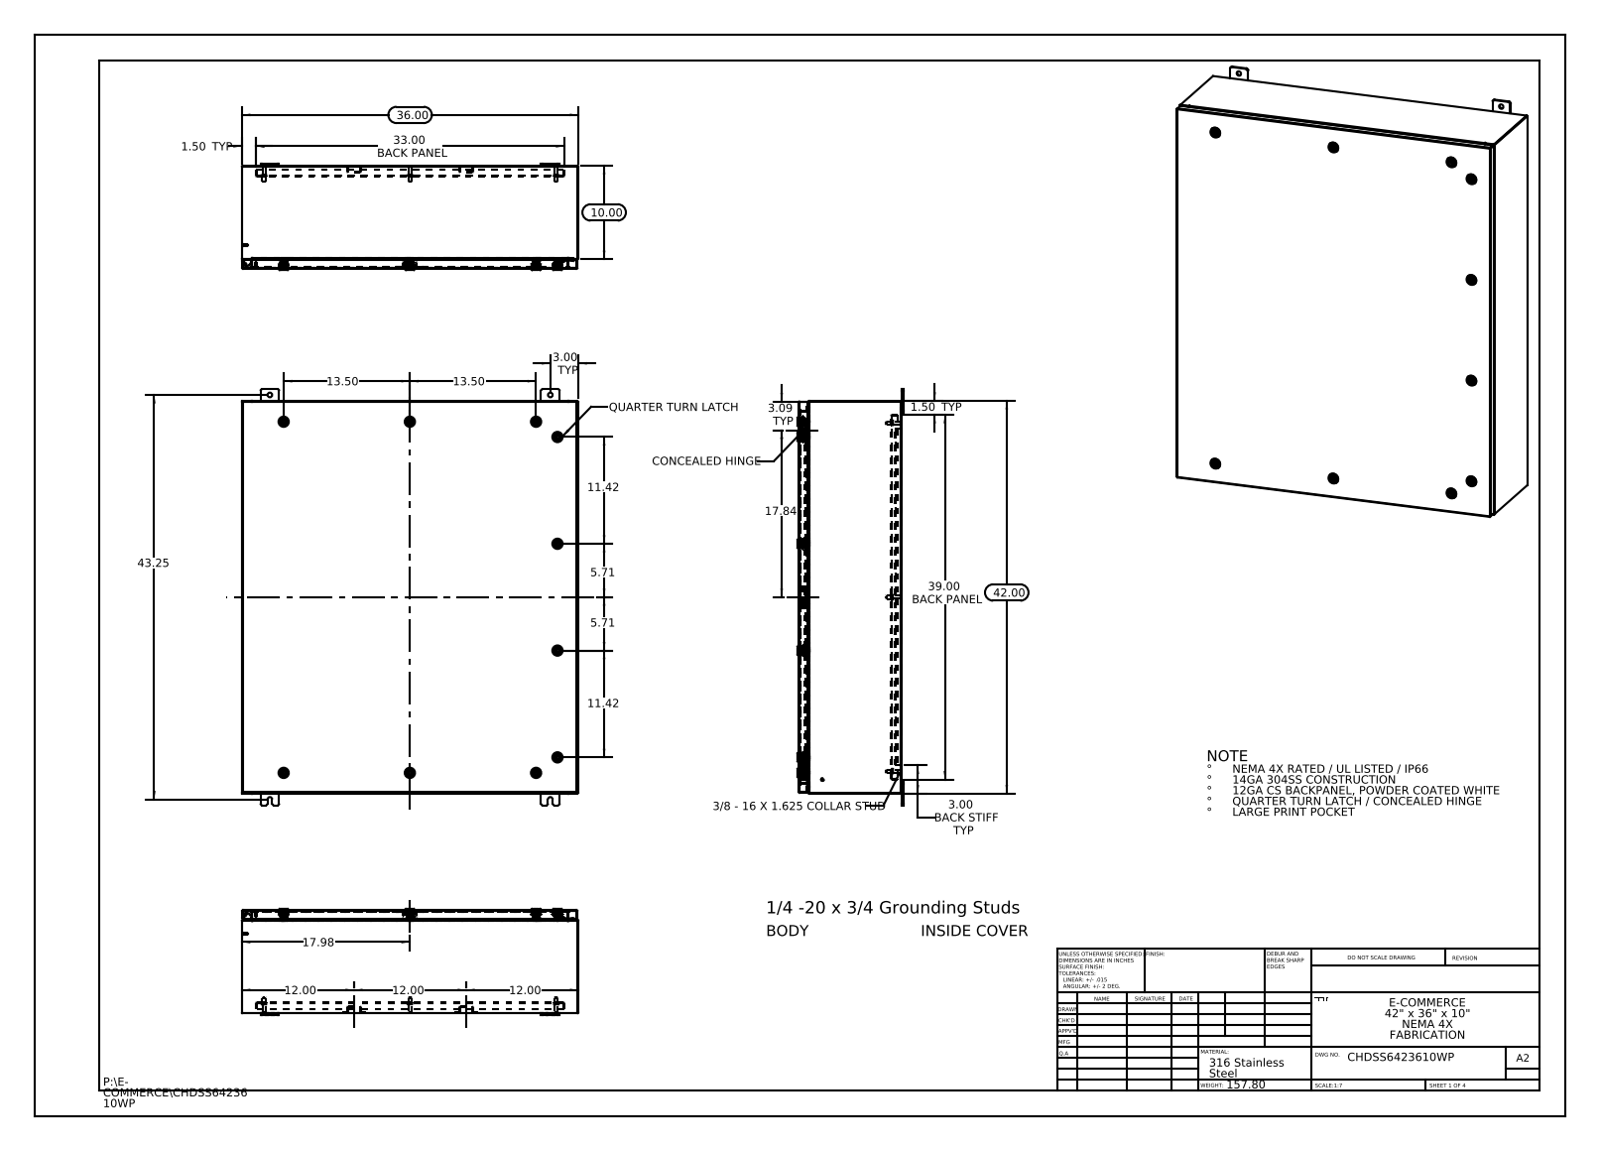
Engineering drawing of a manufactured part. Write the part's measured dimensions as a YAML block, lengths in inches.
part_name: "CHDSS6423610WP Top; CHDSS6423610WP Enclosure Stiffener; CHDSS6423610WP Cover; CHDSS6423610WP Backpanel (+8 more)"
step_written_by: "SolidWorks 2013 (CONFIG_CONTROL_DESIGN)"
units: inches
bodies: {solids: 94, faces: 9060, planar: 2626, cylindrical: 2826, other: 3608}
overall_size: [44.5, 36, 11.356]
volume: 558.3
surface_area: 13851
round_holes:
  - {diameter: 0.5, count: 12}
  - {diameter: 0.197, count: 10}
  - {diameter: 0.394, count: 10}
  - {diameter: 0.4, count: 10}
  - {diameter: 0.63, count: 10}
  - {diameter: 0.787, count: 10}
  - {diameter: 0.136, count: 6}
  - {diameter: 0.25, count: 6}
  - {diameter: 0.211, count: 1}
round_bosses_or_shafts:
  - {diameter: 0.236, count: 12}
  - {diameter: 1.102, count: 10}
  - {diameter: 0.78, count: 10}
  - {diameter: 0.626, count: 10}
  - {diameter: 0.61, count: 10}
  - {diameter: 0.531, count: 10}
  - {diameter: 0.392, count: 10}
  - {diameter: 0.114, count: 10}
partial_cylinders:
  - {radius: 0.006, count: 330}
  - {radius: 0.118, count: 330}
  - {radius: 0.028, count: 120}
  - {radius: 0.02, count: 40}
  - {radius: 0.197, count: 40}
  - {radius: 0.013, count: 34}
  - {radius: 0.088, count: 30}
  - {radius: 0.19, count: 24}
face_to_face_distances: [0.075, 0.074, 10.861, 10.936, 11.01, 10.935, 0.104, 1, 1.075, 9.861]
hole_center_spacings: [13.5, 17, 17.145, 18.625, 24.311, 36.379, 39.903, 40.394]
